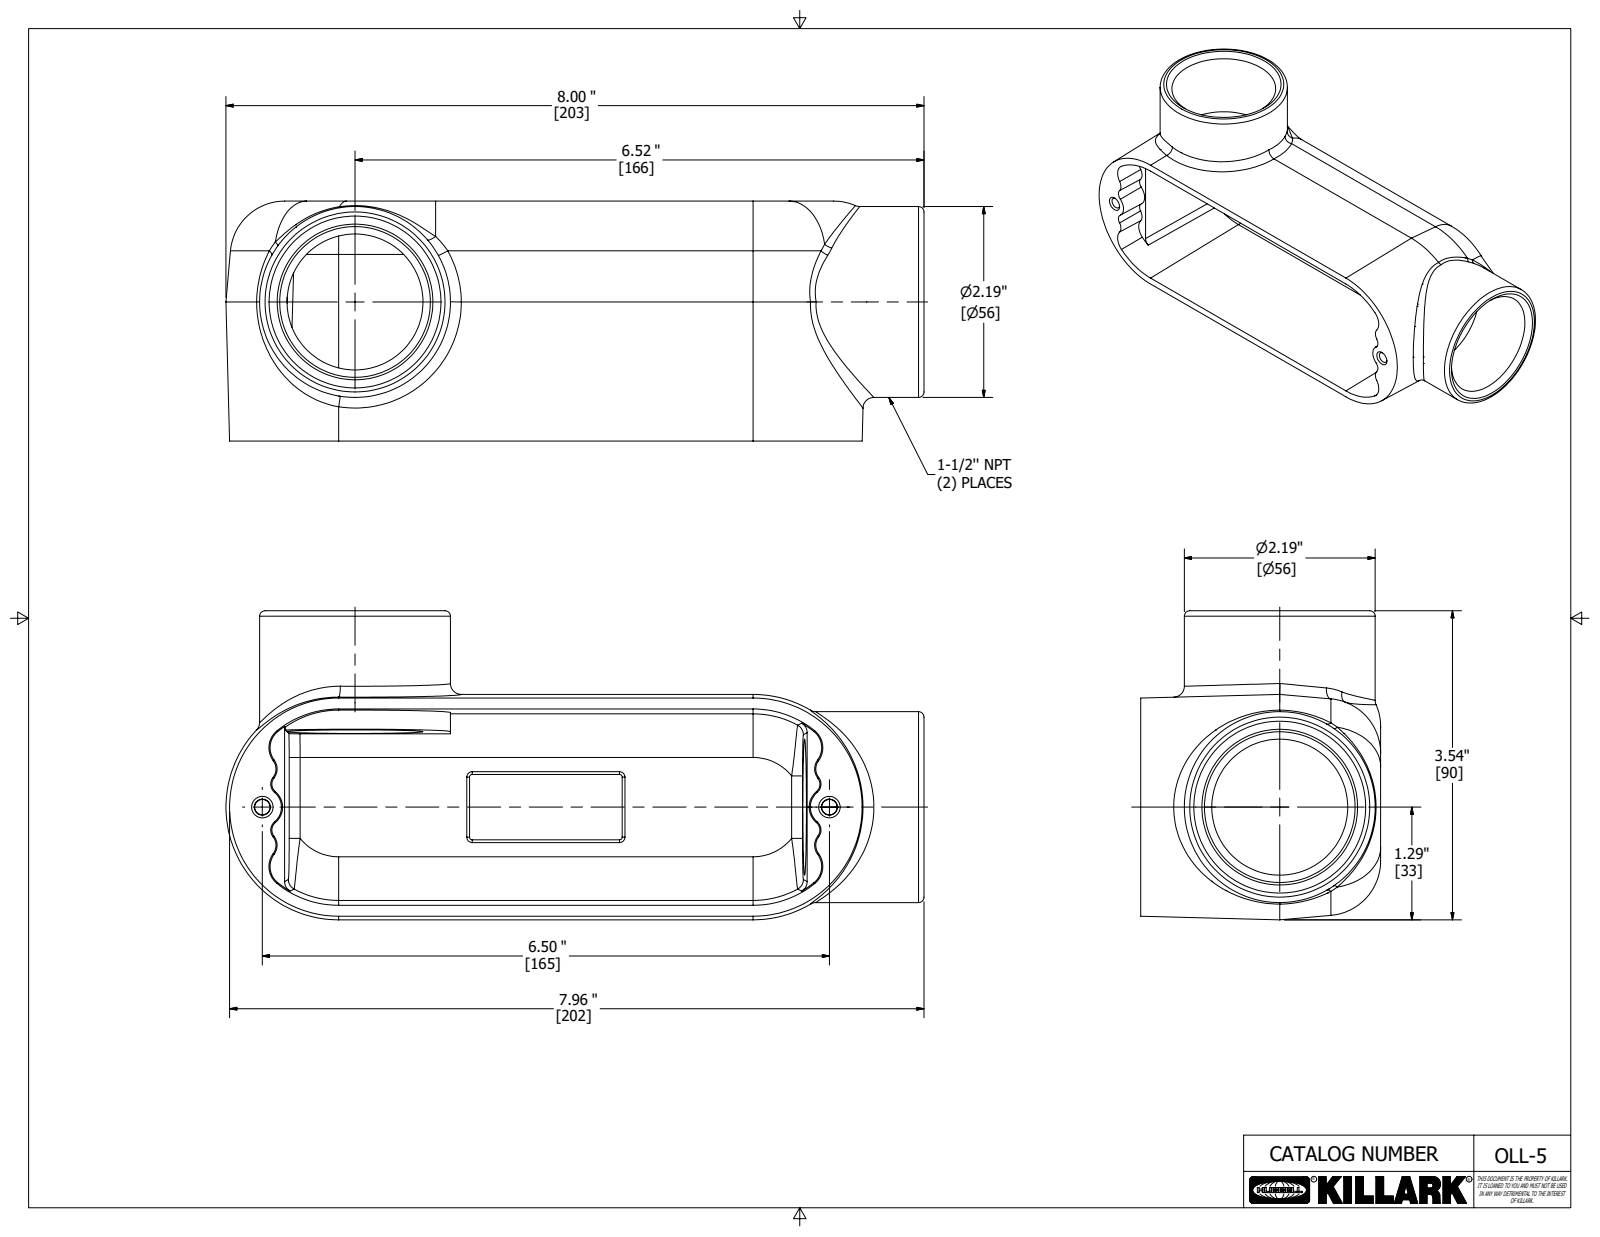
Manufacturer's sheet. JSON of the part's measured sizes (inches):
{"part_name": "18249-1", "step_written_by": "Autodesk Inventor 2018 (AUTOMOTIVE_DESIGN)", "units": "inches", "bodies": {"solids": 1, "faces": 114, "planar": 30, "cylindrical": 11, "other": 73}, "overall_size": [8.001, 3.542, 2.75], "volume_in3": 13.33, "surface_area_in2": 134.9, "round_holes": [[1.558, 2]], "round_bosses_or_shafts": [[2.187, 2]], "partial_cylinders_radius": [[0.125, 2], [0.5, 2], [0.625, 2]], "face_to_face_distances": [2.375, 0.125, 2.75, 2.625, 0.219, 2.156, 0.156, 0.031, 2.594, 0.031]}
